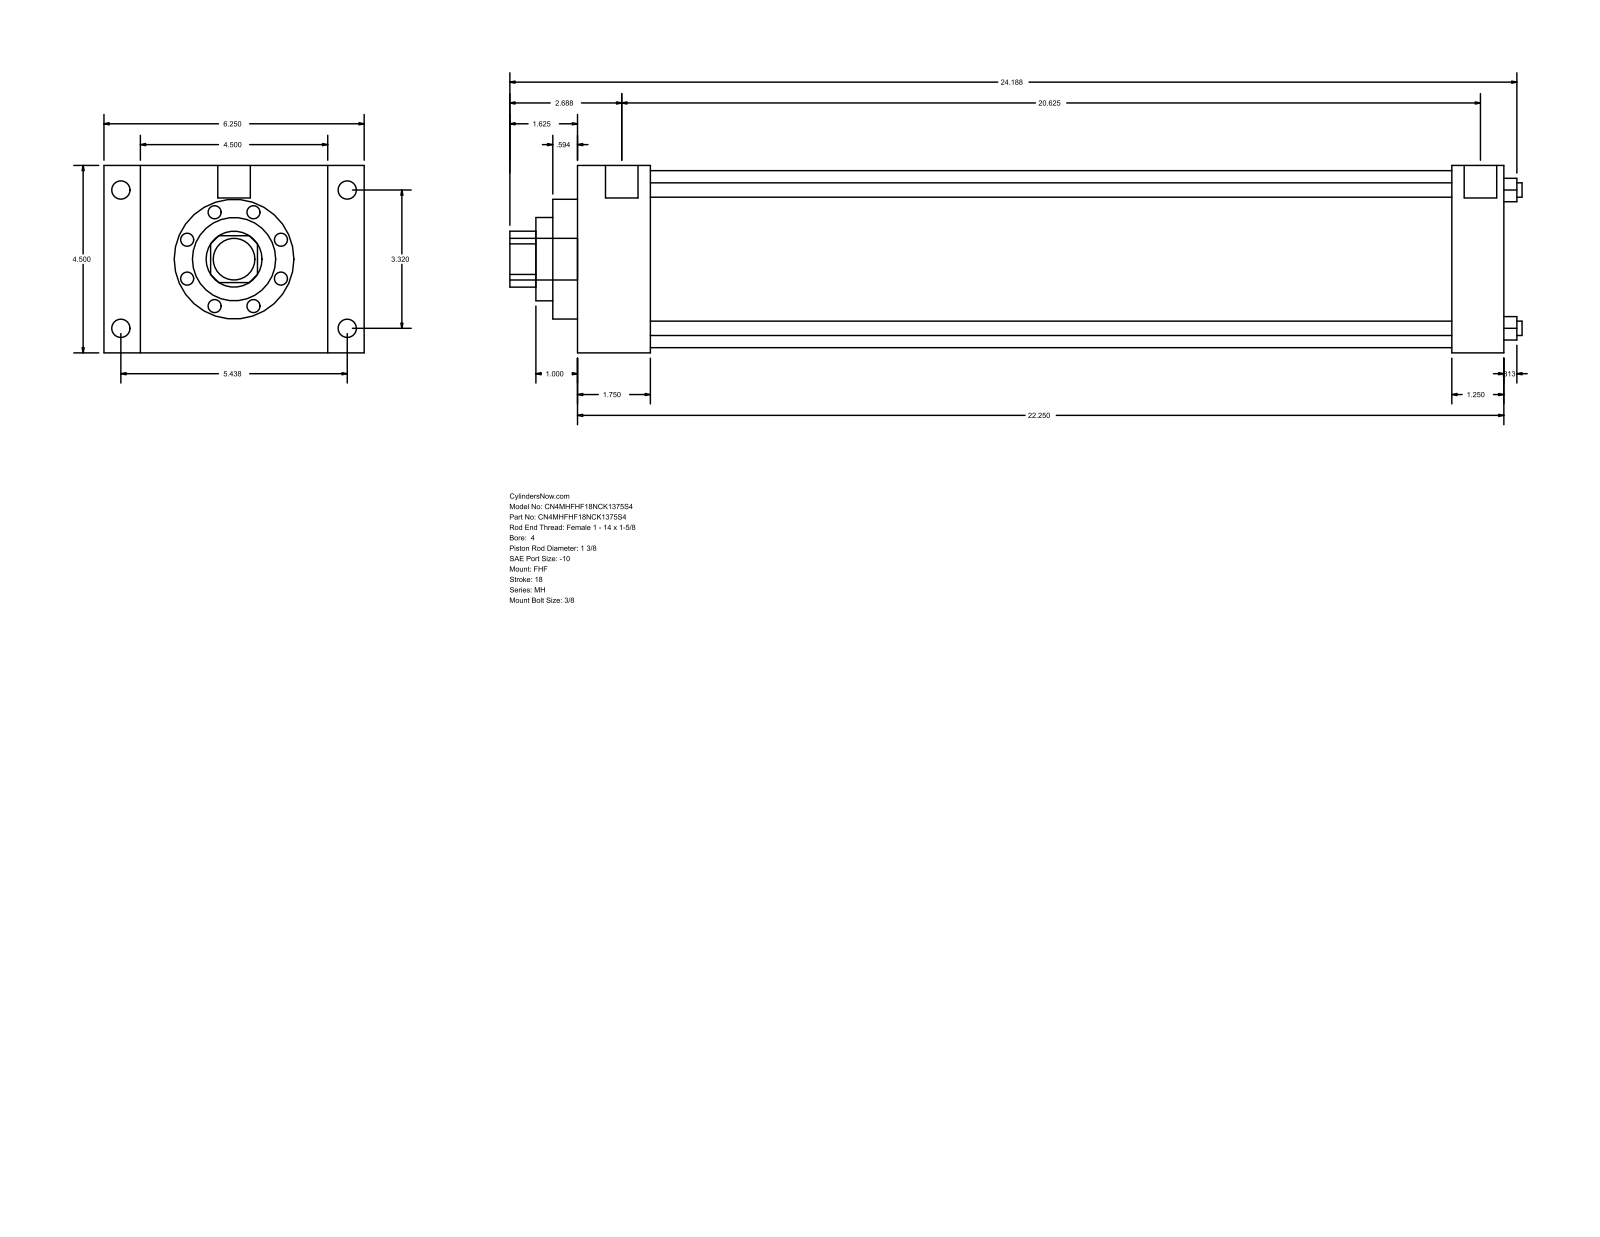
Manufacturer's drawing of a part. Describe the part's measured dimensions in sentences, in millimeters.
The part is named "MH_FHF__0400_1.375". Its 3-D file was written by "GSSL Pune (CONFIG_CONTROL_DESIGN)". It is 0 solids with 90 faces: 61 planar, 29 cylindrical and 0 other. Overall it measures 617.54 by 158.75 by 114.3 millimeters. Round holes: 4 of diameter 8.76, 1 of diameter 34.92, 1 of diameter 50.8, 1 of diameter 73.03, 1 of diameter 107.95. Round bosses or shafts: 4 of diameter 11.13, 4 of diameter 8.73, 2 of diameter 19.84, 1 of diameter 25.4. Partial cylindrical surfaces (rounded edges, fillets, slot ends): 1 of radius 17.06. The main face-to-face distances are 114.3, 565.15, 44.45, 520.7, 22.23, 136.53, 158.76, 533.4, 488.95, 31.75. The hole center spacings are 59.62, 84.32, 119.25.
